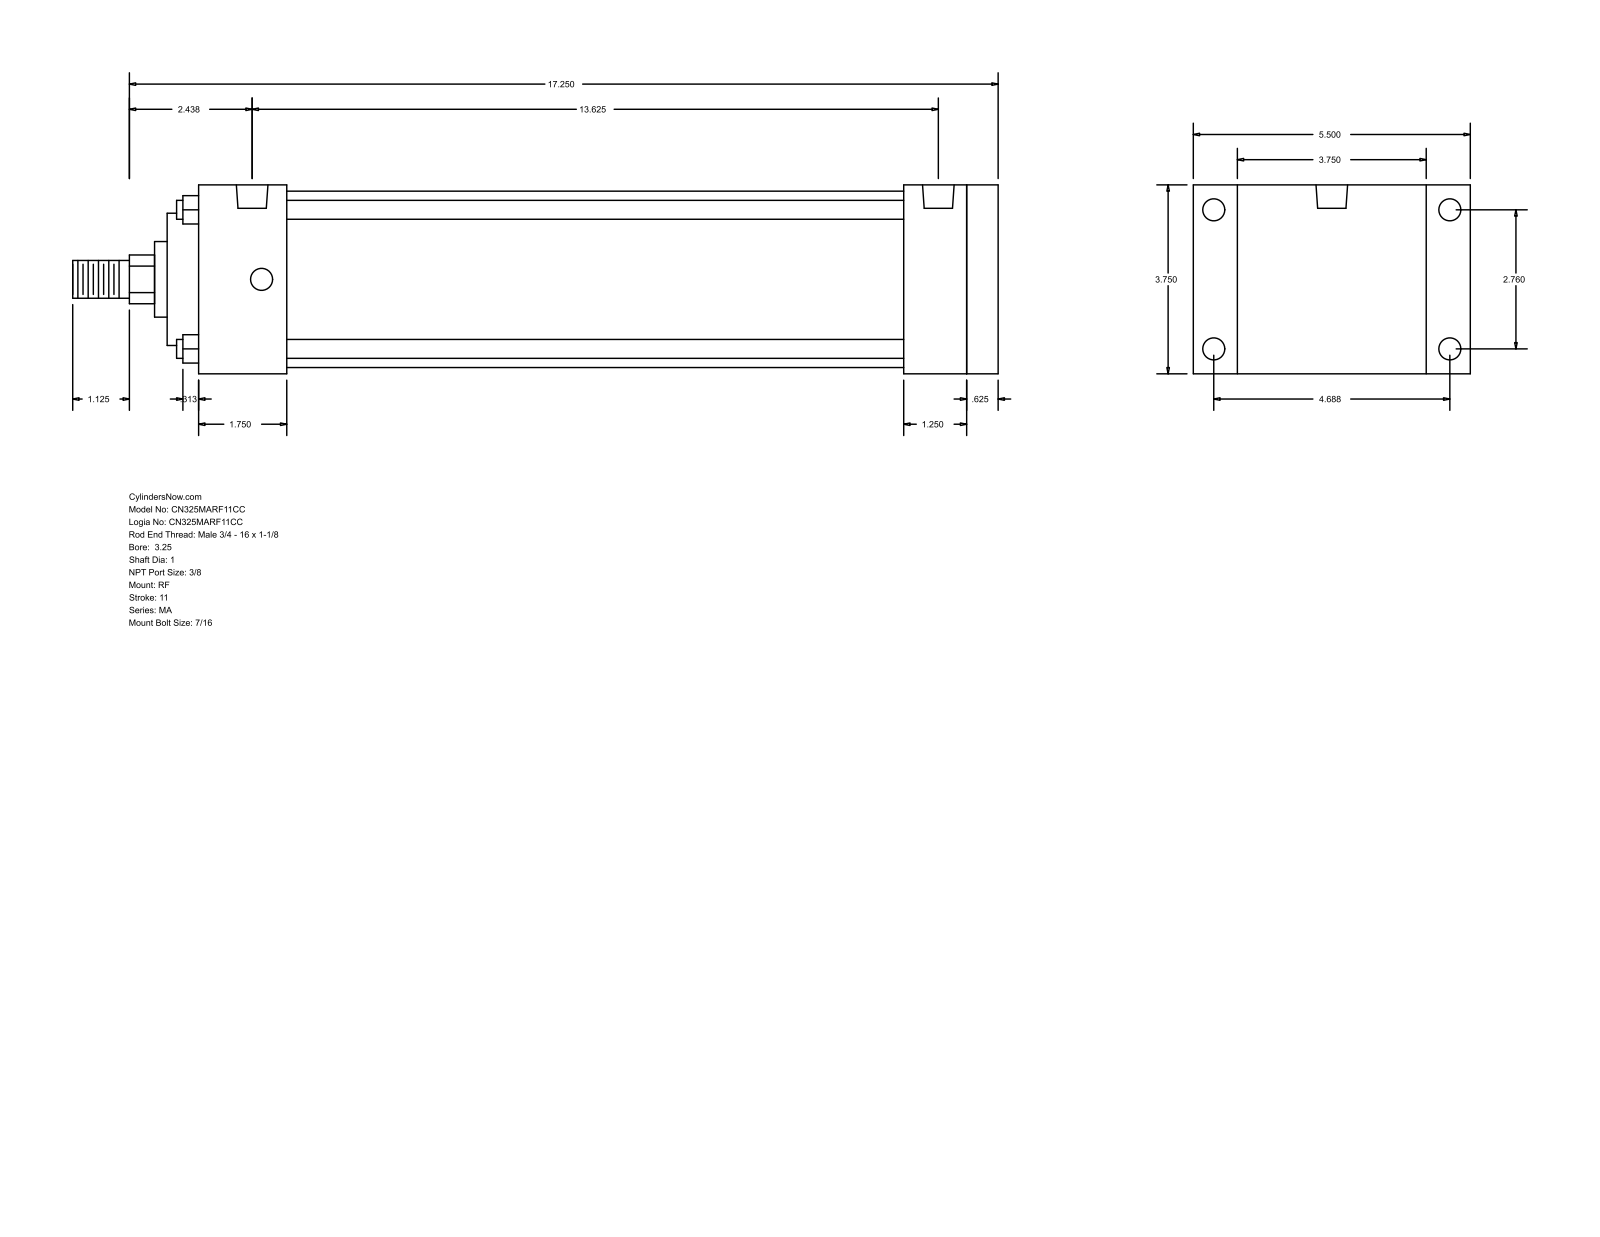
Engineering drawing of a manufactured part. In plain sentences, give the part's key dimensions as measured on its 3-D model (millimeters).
The part is named "MA_RF__0325_1". Its 3-D file was written by "GSSL Pune (CONFIG_CONTROL_DESIGN)". It is 0 solids with 94 faces: 65 planar, 29 cylindrical and 0 other. Overall it measures 466.73 by 139.7 by 95.25 millimeters. Round holes: 8 of diameter 11.11, 2 of diameter 15.93. Round bosses or shafts: 4 of diameter 9.53, 1 of diameter 88.9, 1 of diameter 66.67, 1 of diameter 38.1, 1 of diameter 25.4, 1 of diameter 19.05. Partial cylindrical surfaces (rounded edges, fillets, slot ends): 1 of radius 12.29. The main face-to-face distances are 95.24, 403.23, 387.35, 15.88, 22.23, 117.47, 355.6, 31.75, 47.63, 44.46. The hole center spacings are 4.76, 70.1, 119.06, 138.16, 336.56, 341.32, 346.08.
